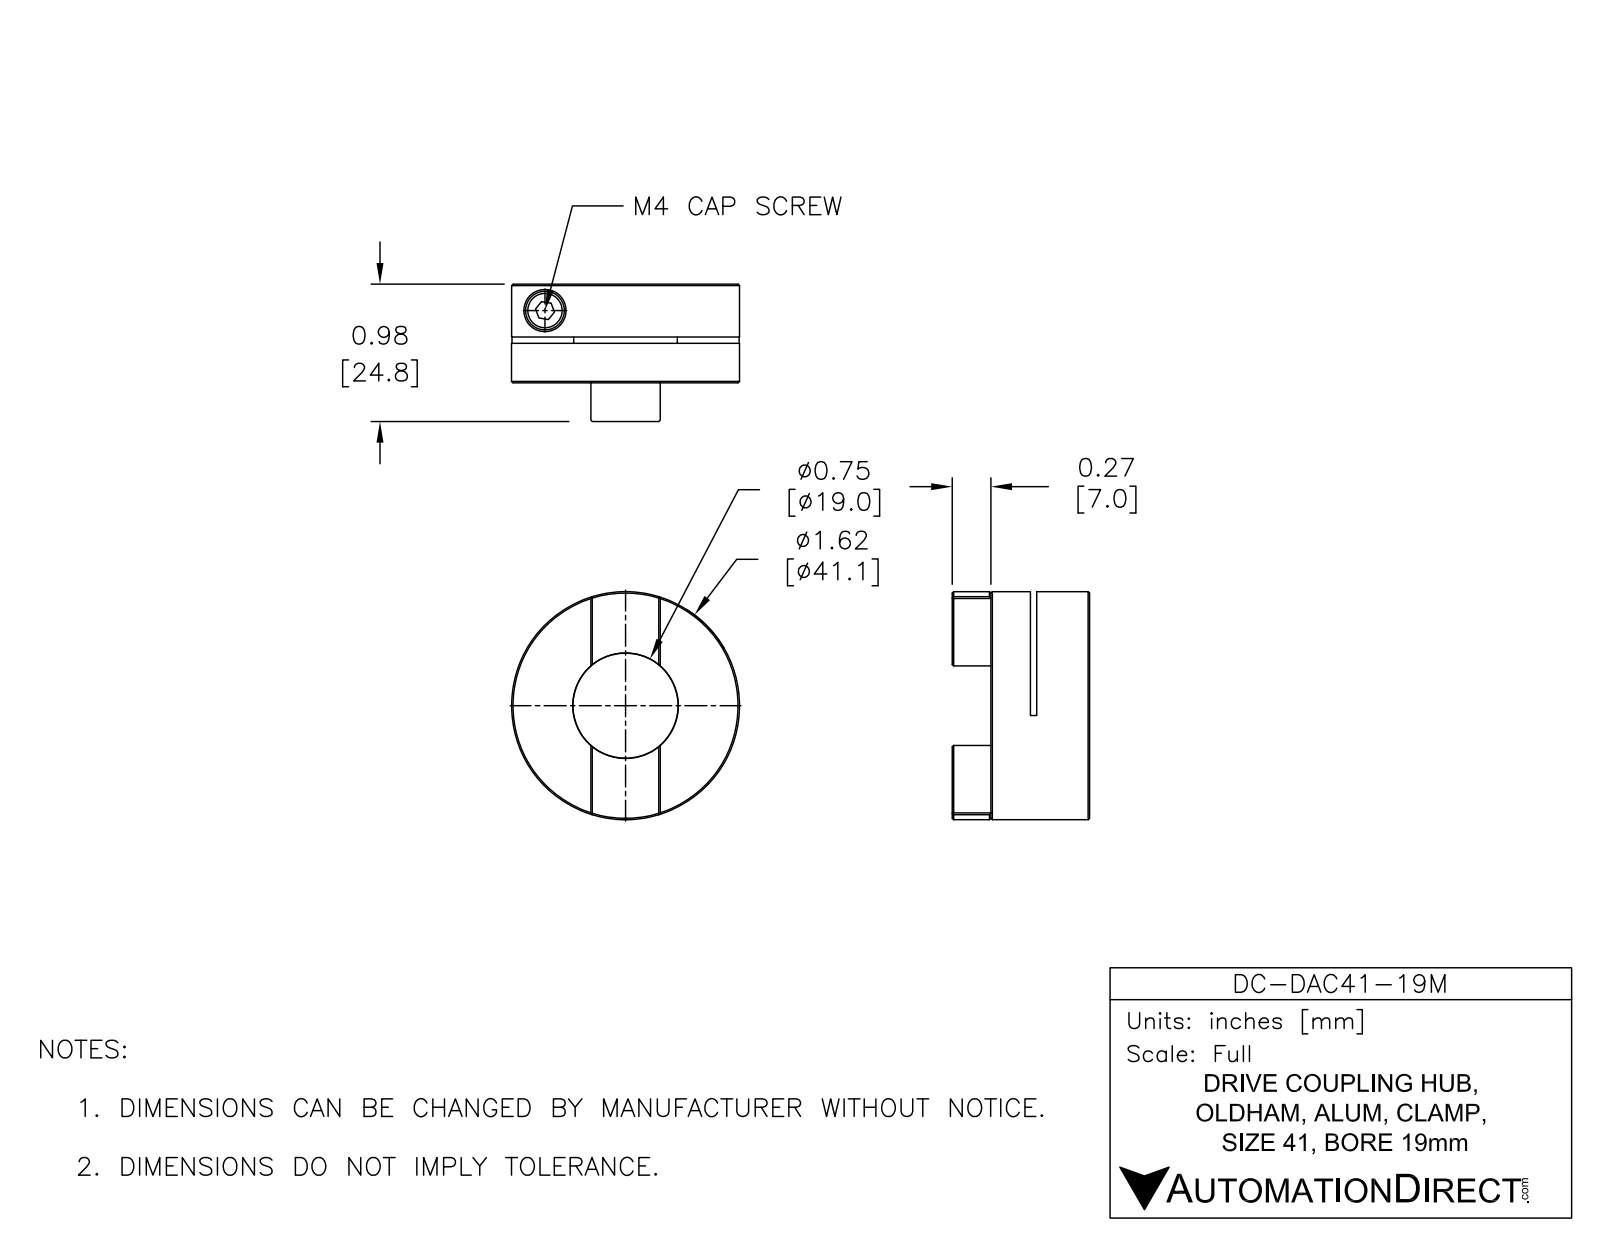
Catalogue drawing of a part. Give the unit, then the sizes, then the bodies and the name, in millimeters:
Units: millimetres
Overall size (bounding box): 41.15 × 41.15 × 24.78
Round holes (diameter × count): ⌀3.99 ×1, ⌀7.62 ×1, ⌀19 ×1
Round bosses / shafts (diameter × count): ⌀41.15 ×1
Partial cylindrical surfaces — rounded edges, fillets, slot ends (radius × count): R22.23 ×1
Main face-to-face distances: 17.8, 7.14, 10.66, 8.28, 1.14, 9.52, 6.97, 14.11, 15.25, 24.77
Volume: 19 136 mm³ · Surface area: 7 772 mm²
Bodies: 1 solid, 52 faces (27 planar, 15 cylindrical, 10 other)
Part name (STEP PRODUCT): DC-DAC41-19M
STEP written by: SolidWorks 2015 (AUTOMOTIVE_DESIGN)
